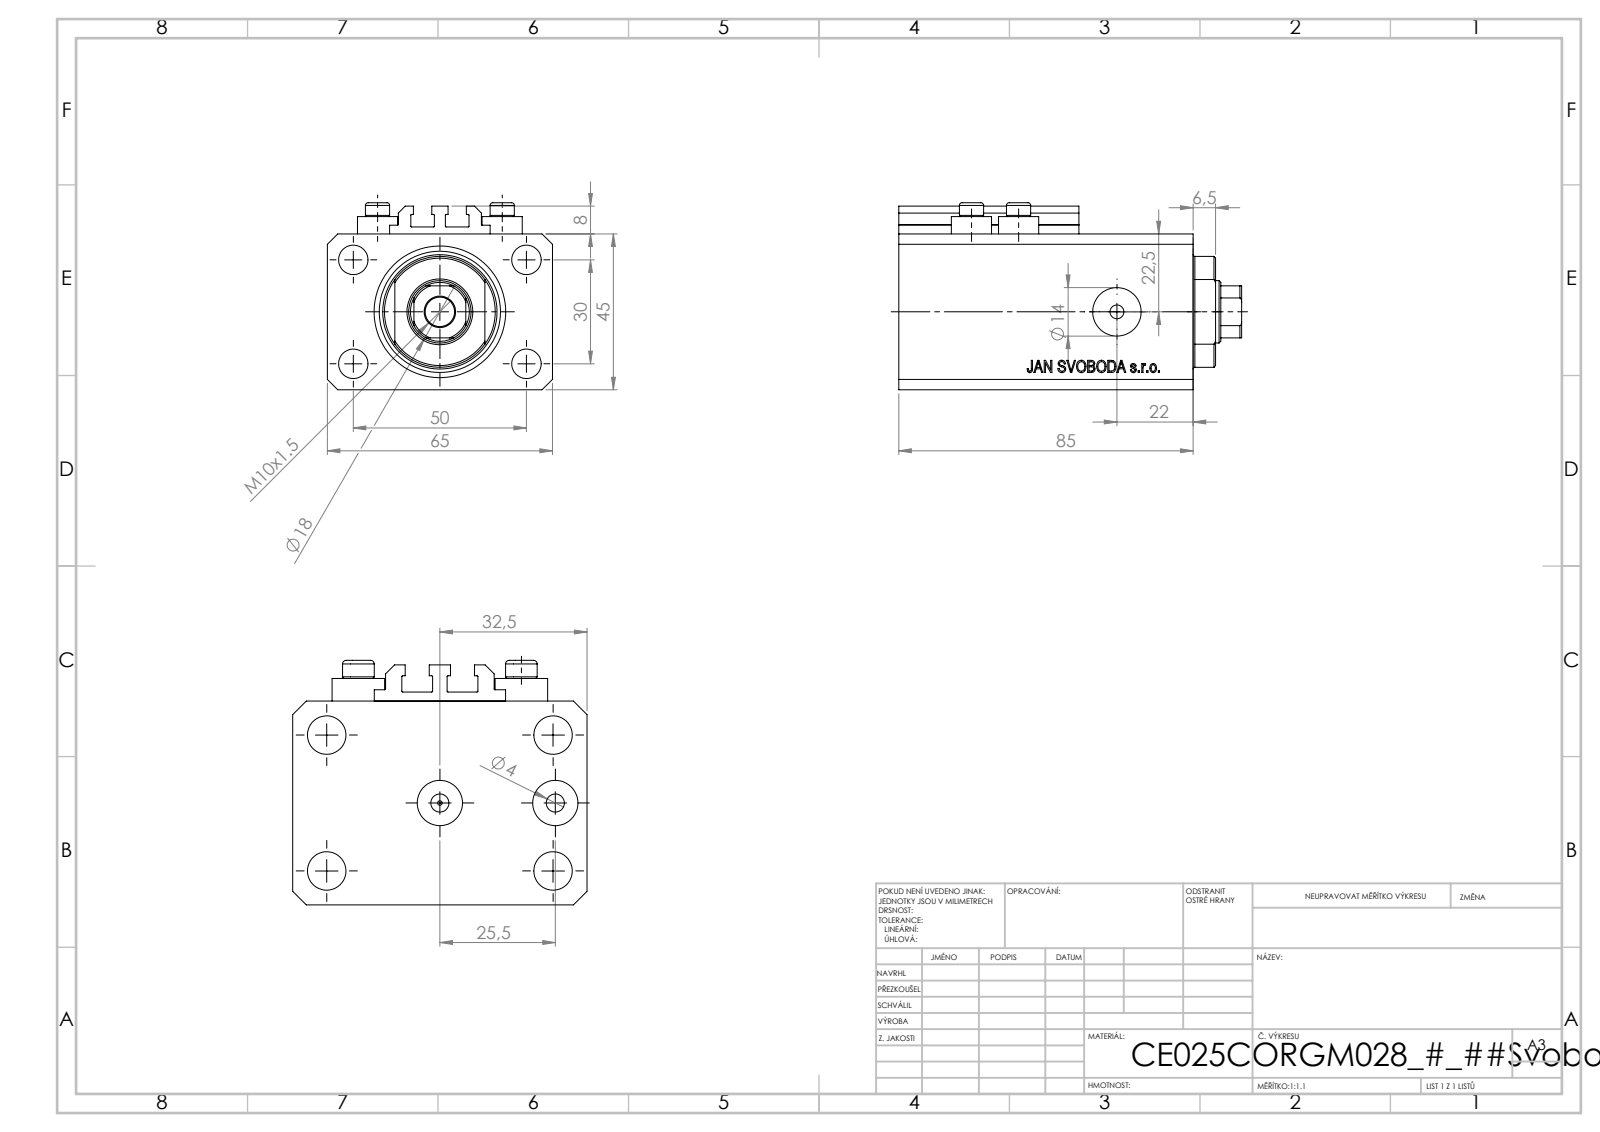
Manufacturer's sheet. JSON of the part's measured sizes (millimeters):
{"part_name": "V250CE_C_VCP; V250CE_VC_C; V250CE_C_Body; ALLEN BOLT V250CE", "step_written_by": "SolidWorks 2019 (CONFIG_CONTROL_DESIGN)", "units": "millimeters", "bodies": {"solids": 8, "faces": 1042, "planar": 504, "cylindrical": 92, "other": 446}, "overall_size": [99, 65, 54], "volume_mm3": 232059, "surface_area_mm2": 62126, "round_holes": [[4, 8], [8.5, 5], [10, 2], [14, 2], [1.25, 1], [18, 1], [25, 1], [38, 1]], "round_bosses_or_shafts": [[11.6, 4], [7, 4]], "partial_cylinders_radius": [[0.2, 10], [8.5, 1], [16, 1]], "face_to_face_distances": [45, 65, 14, 85, 71, 47, 6.9, 64.1, 78.1, 3], "hole_center_spacings": [29.15, 13.6, 15.01, 30, 36, 38.48, 50, 52.68]}
